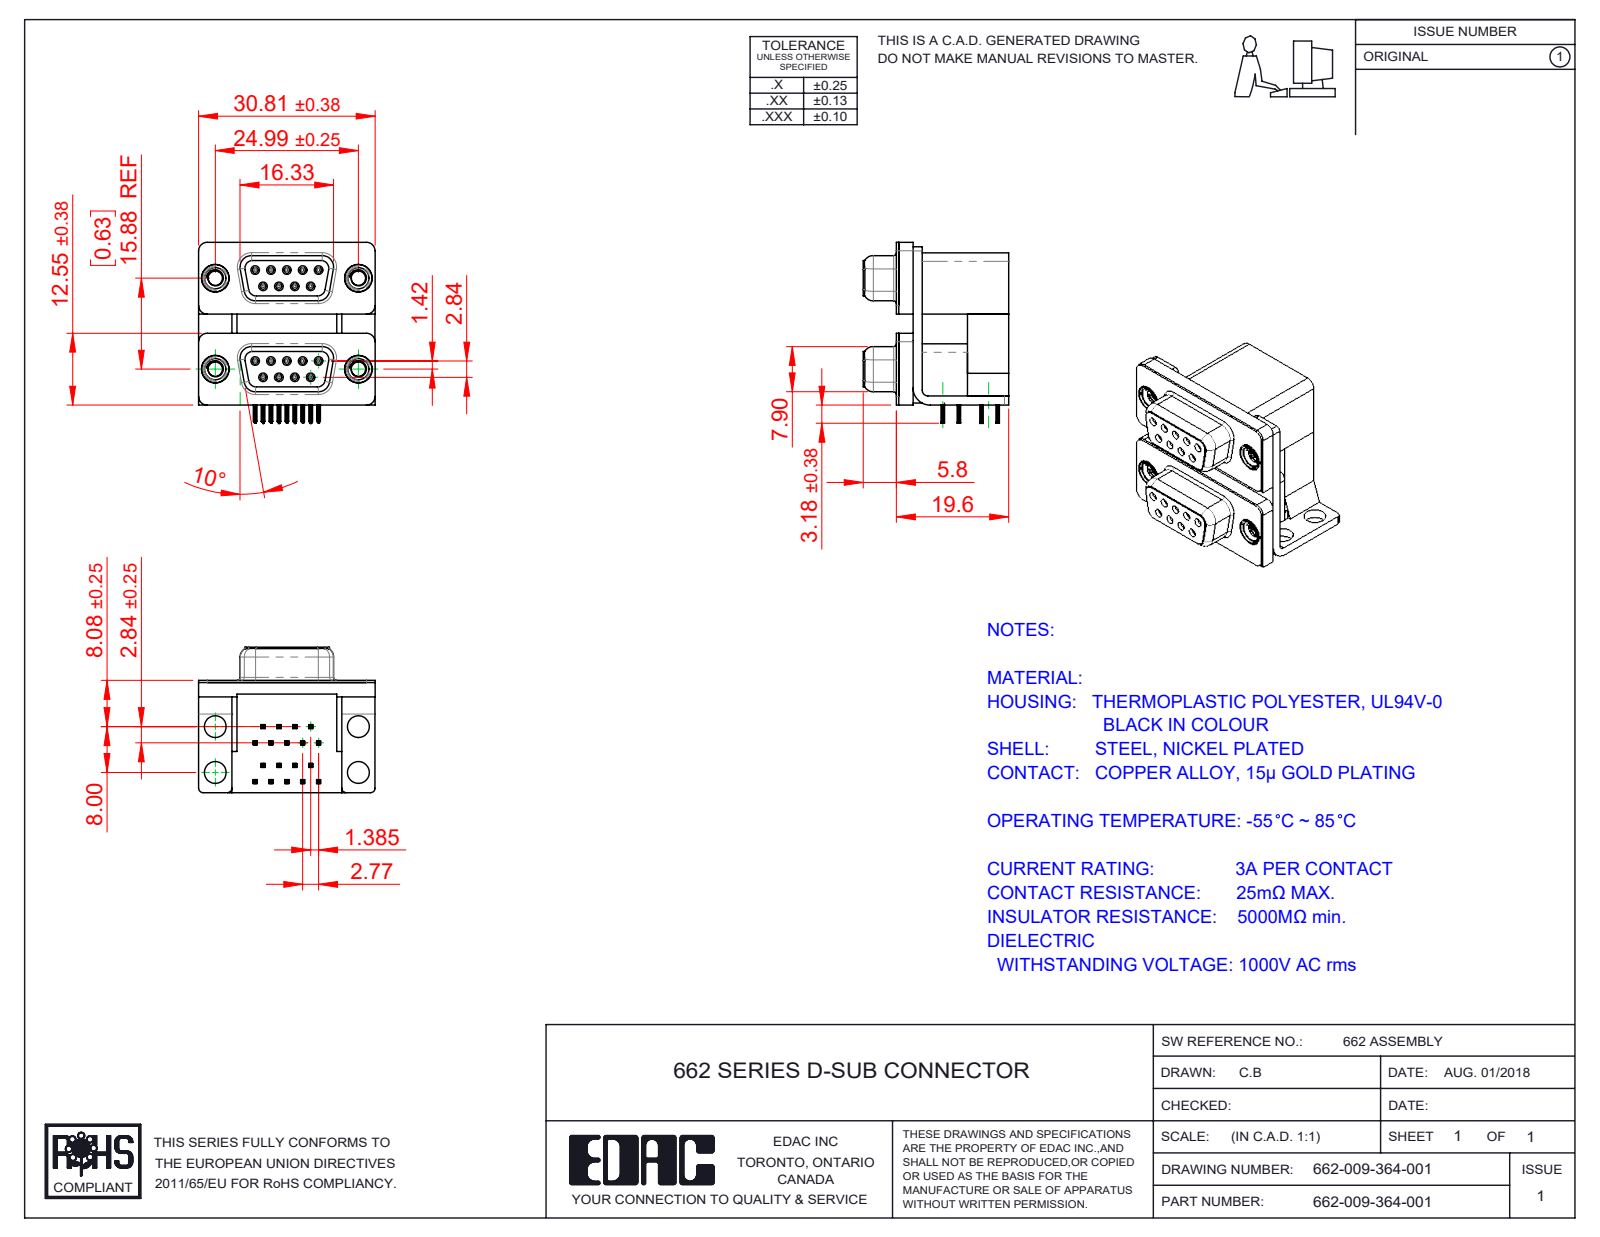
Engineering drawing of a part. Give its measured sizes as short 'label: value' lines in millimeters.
name: 662 Housing Lower_09 Contacts; 662 Housing Spacer_09 Contacts L; 662-009-364-001; 662 Threaded Rivet_M3 (+7 more)
written by: SolidWorks 2020 (CONFIG_CONTROL_DESIGN)
unit: mm
bodies: 29 solids, 3114 faces (1374 planar, 804 cylindrical, 936 other)
size: 31.61 × 30.81 × 25.4
volume: 10 817 mm³; area: 12 758 mm²
holes: 18× ⌀0.8, 18× ⌀0.9, 4× ⌀2.5, 4× ⌀3.5, 4× ⌀3.8, 4× ⌀4, 4× ⌀4.8, 4× ⌀5
bosses: 18× ⌀1.2, 4× ⌀4.9, 4× ⌀4.75, 4× ⌀3.9
rounds: 144× R0.1, 72× R0.15, 36× R0.35, 18× R0.34, 18× R1.35, 12× R1.5, 8× R0.28, 8× R0.5
face distances: 0.4, 2.5, 16.7, 19.2, 15.88, 2.9, 19.6, 7.2, 9.5, 12
hole spacings: 3.16, 2.77, 16.12, 15.88, 5.54, 16.82, 13.11, 18.77
